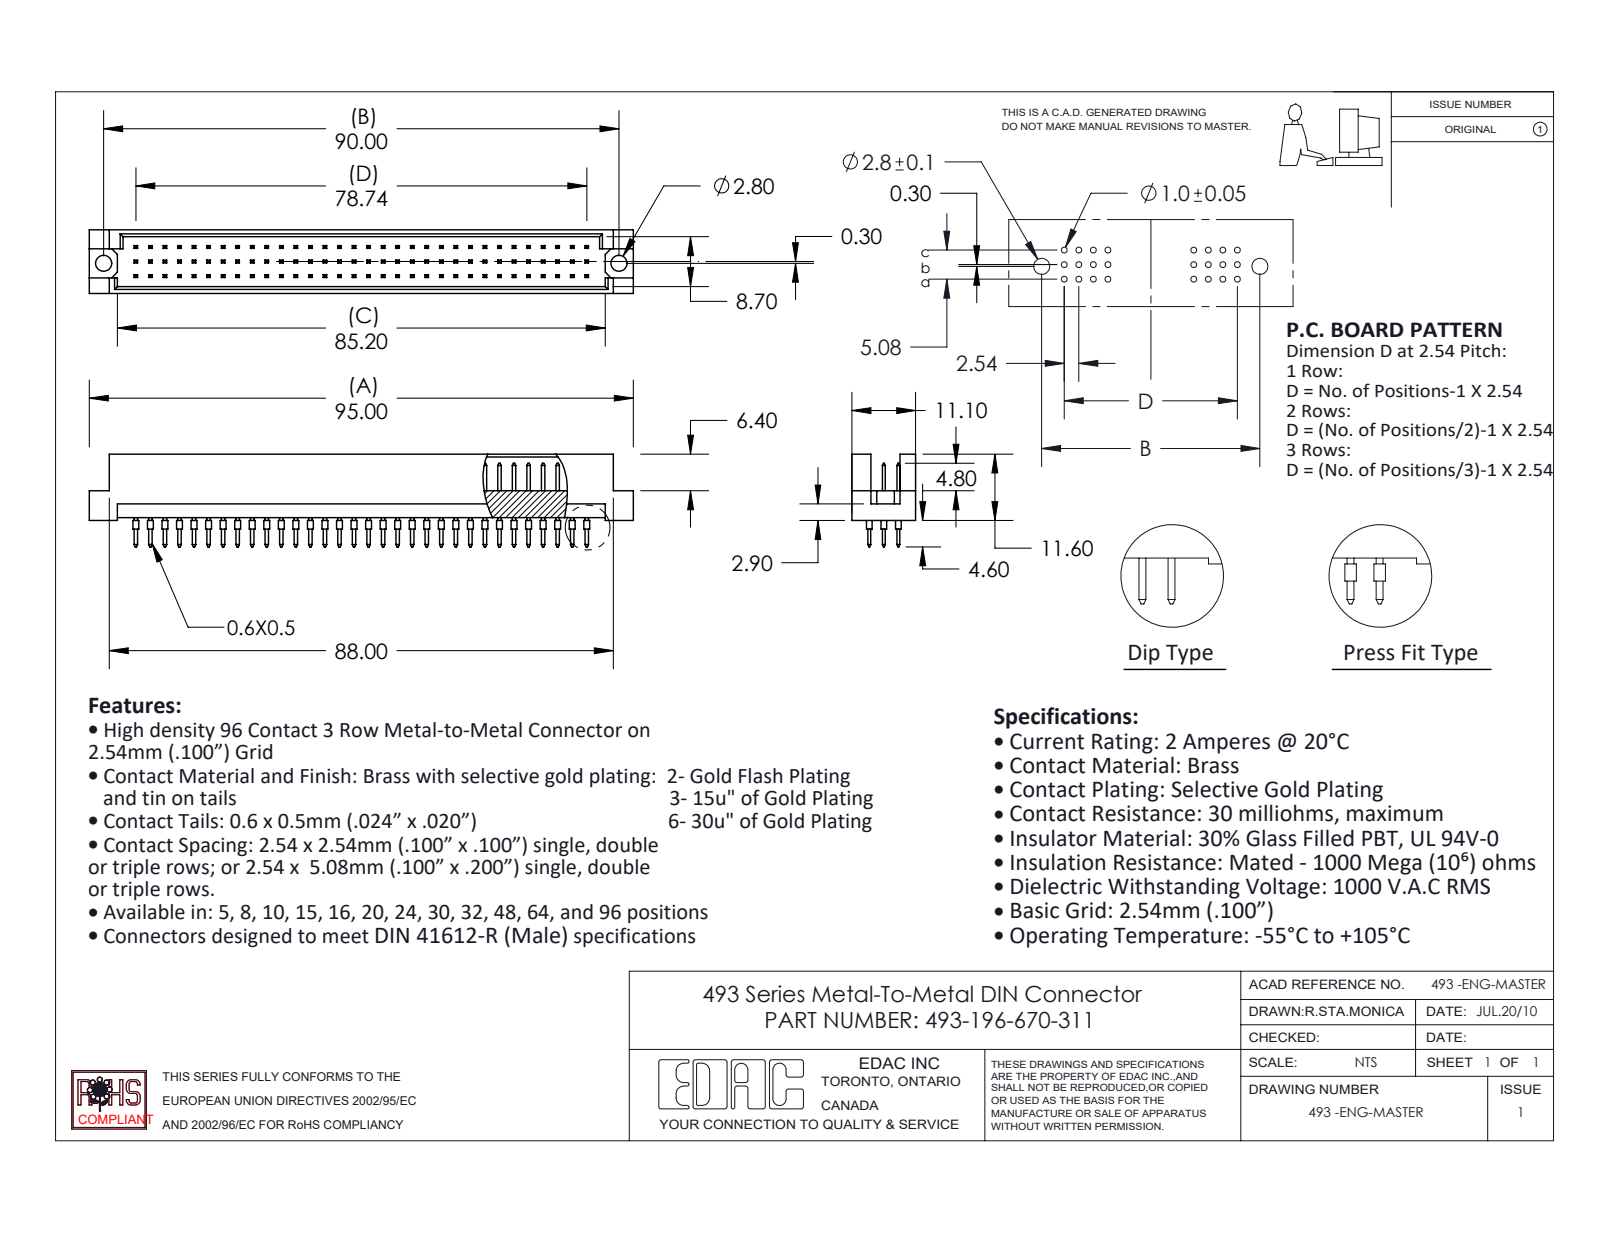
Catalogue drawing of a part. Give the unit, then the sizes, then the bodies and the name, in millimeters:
Units: millimetres
Overall size (bounding box): 95 × 16.2 × 11.1
Round holes (diameter × count): ⌀2.8 ×2
Round bosses / shafts (diameter × count): ⌀1 ×96
Main face-to-face distances: 2.54, 1.2, 9.9, 0.5, 5.08, 11.1, 8.7, 4.7, 4.6, 2.76
Hole centre spacings: 90
Volume: 6 138 mm³ · Surface area: 9 749 mm²
Bodies: 97 solids, 2548 faces (2352 planar, 196 cylindrical, 0 other)
Part name (STEP PRODUCT): 493 Part_96; 493-196-670-311; 493-290_70
STEP written by: SolidWorks 2020 (CONFIG_CONTROL_DESIGN)
